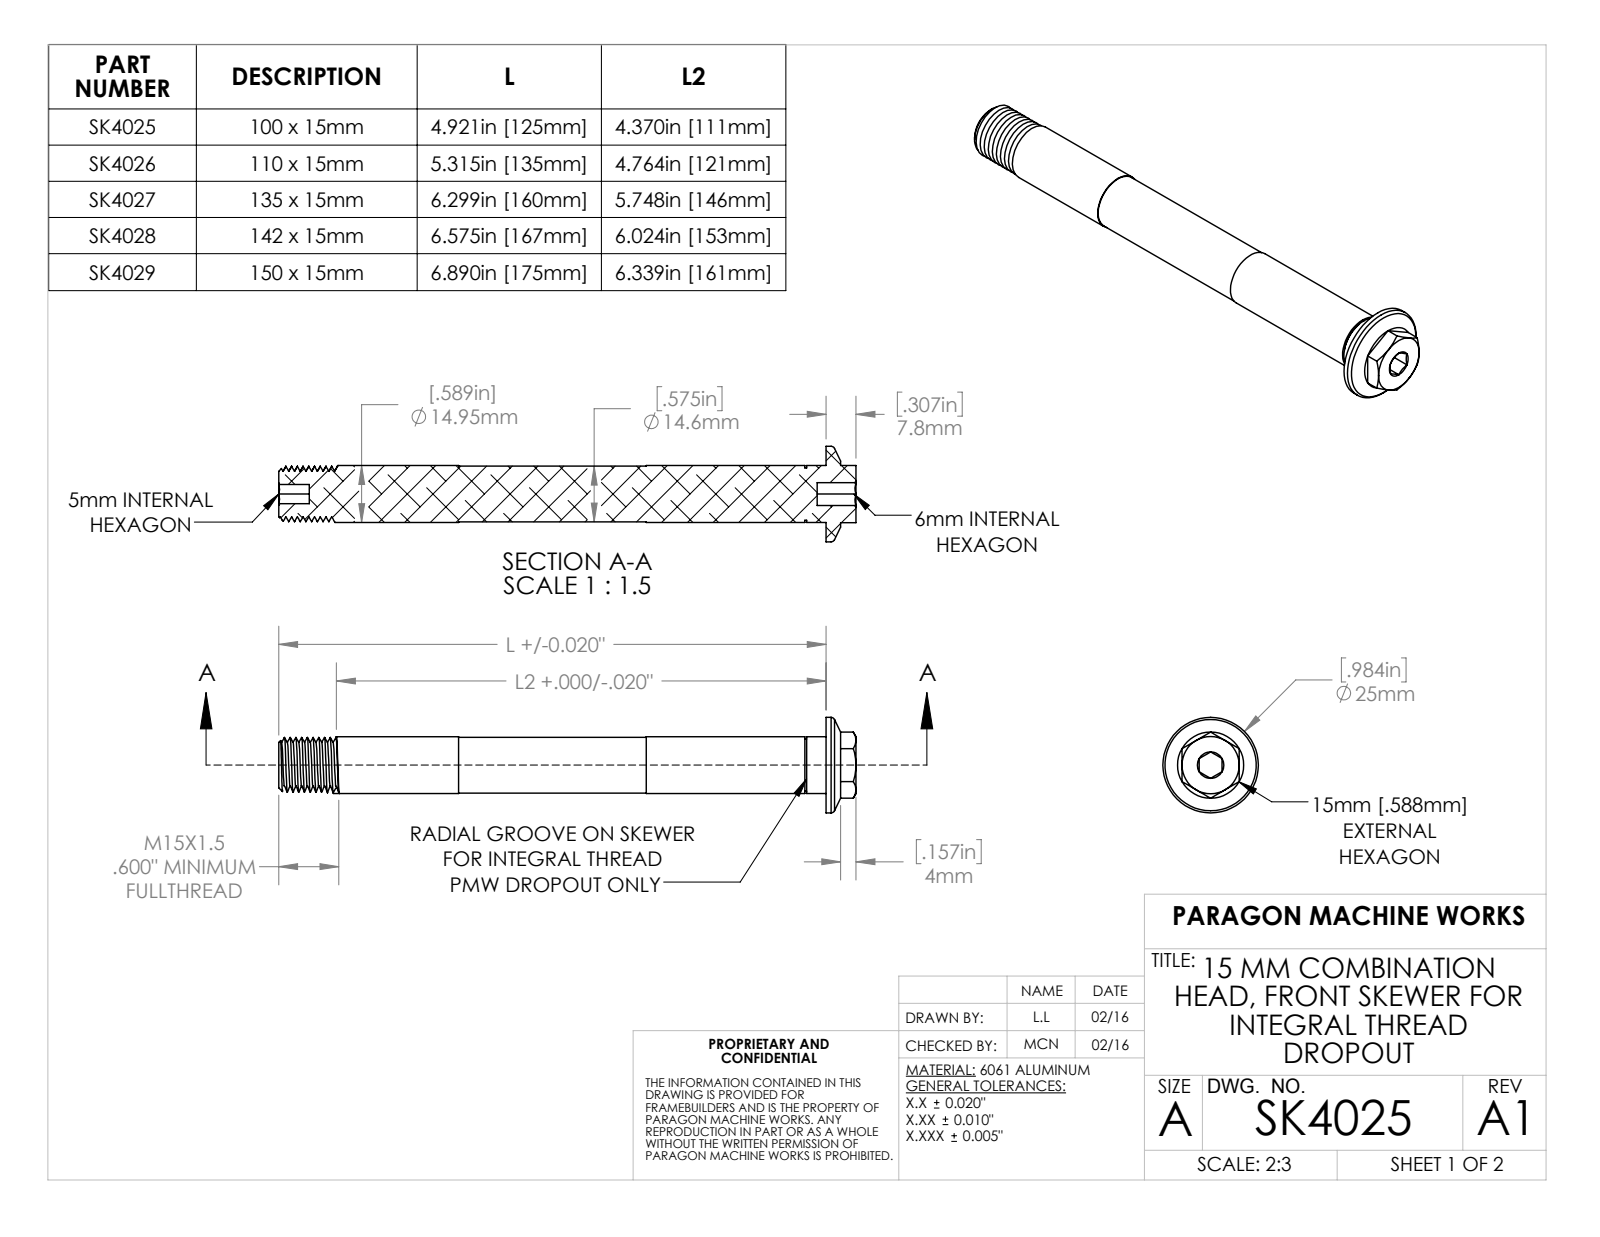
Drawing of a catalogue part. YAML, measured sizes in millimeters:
part_name: "SK4025"
step_written_by: "SolidWorks 2023 (AUTOMOTIVE_DESIGN)"
units: millimeters
bodies: {solids: 1, faces: 82, planar: 36, cylindrical: 15, other: 31}
overall_size: [132.81, 25, 25]
volume: 22826
surface_area: 8099
round_bosses_or_shafts:
  - {diameter: 25, count: 1}
  - {diameter: 14.91, count: 1}
  - {diameter: 14.61, count: 1}
  - {diameter: 13.72, count: 1}
  - {diameter: 11.9, count: 1}
face_to_face_distances: [5, 4.5, 10.5, 0.5, 7.81, 10, 5.5, 6, 15, 125]
